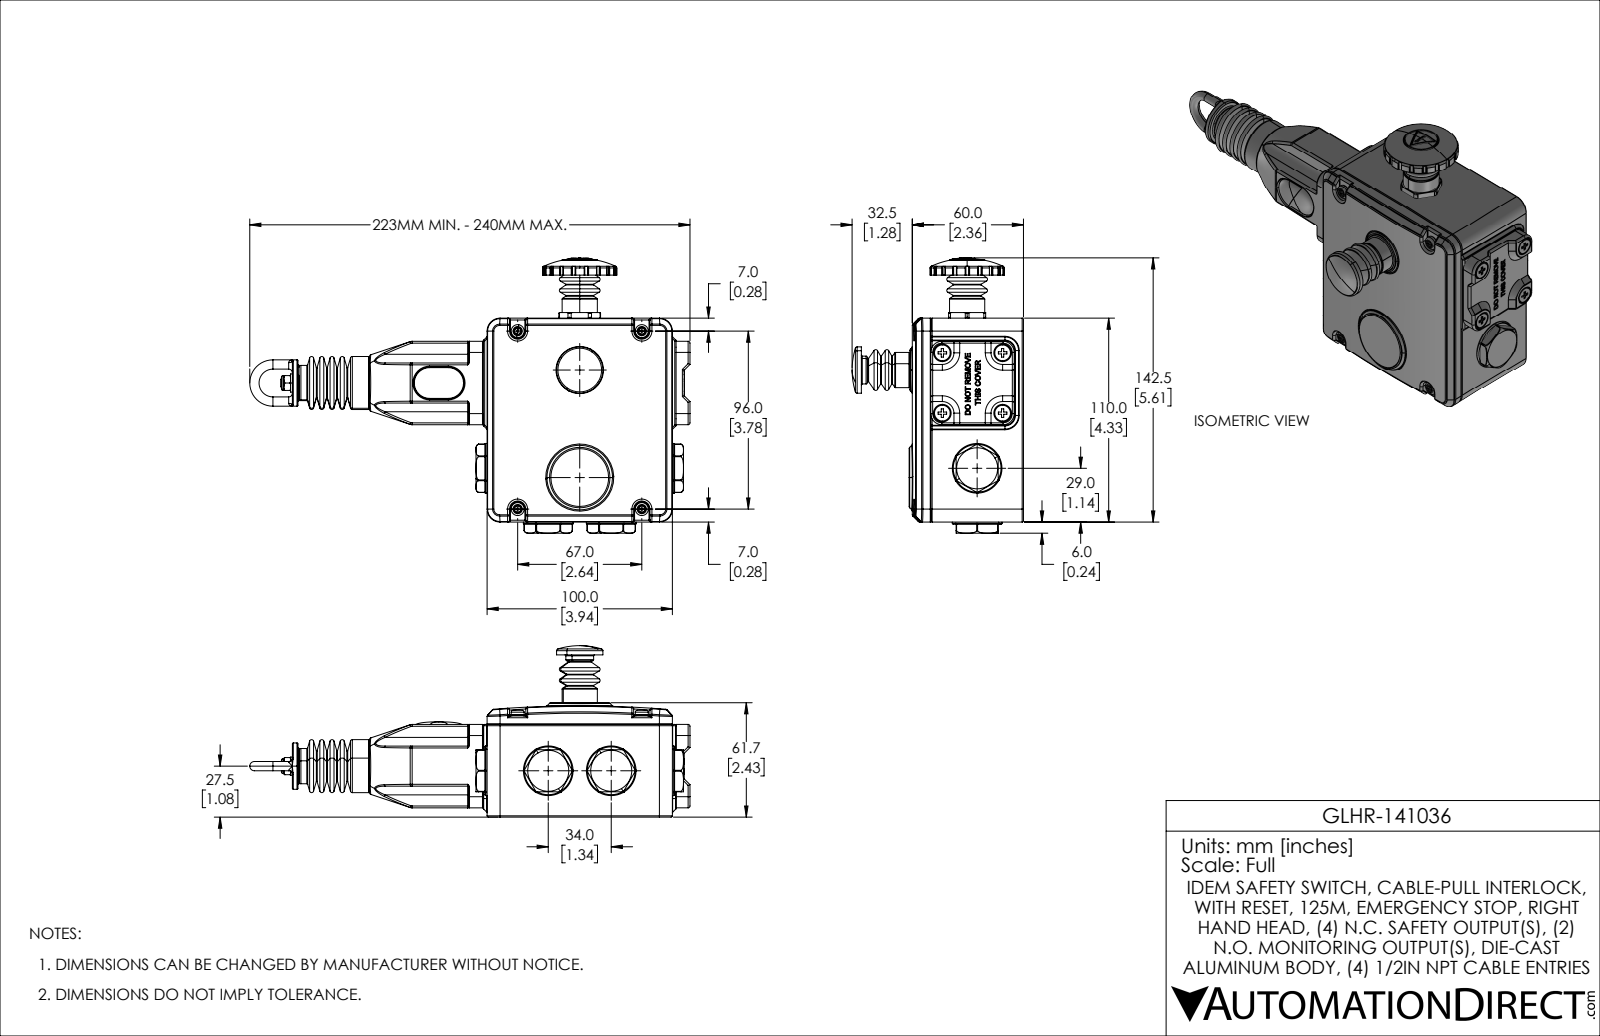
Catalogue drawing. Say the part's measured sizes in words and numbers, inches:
The part is named "GLHR-141036". Its 3-D file was written by "SolidWorks 2021 (AUTOMOTIVE_DESIGN)". It is 32 solids with 4131 faces: 1092 planar, 1371 cylindrical and 1668 other. Overall it measures 9.354 by 5.847 by 3.642 inches. Its volume is 18.02 cubic inches and its surface area 275.6 square inches. Round holes: 11 of diameter 0.197, 9 of diameter 0.209, 7 of diameter 0.374, 6 of diameter 0.354, 4 of diameter 0.13, 4 of diameter 0.157, 4 of diameter 0.189, 4 of diameter 0.213, 4 of diameter 0.228, 3 of diameter 0.118, 3 of diameter 0.173, 3 of diameter 0.504. Round bosses or shafts: 7 of diameter 0.335, 7 of diameter 0.236, 7 of diameter 0.173, 6 of diameter 0.197, 5 of diameter 0.276, 4 of diameter 0.138, 4 of diameter 0.051, 3 of diameter 1.055. Partial cylindrical surfaces (rounded edges, fillets, slot ends): 226 of radius 0.02, 154 of radius 0.039, 136 of radius 0.008, 72 of radius 0.028, 20 of radius 0.012, 14 of radius 0.006, 12 of radius 0.236, 11 of radius 0.004. The main face-to-face distances are 0.138, 2.157, 0.114, 2.043, 4.331, 0.055, 0.157, 4.016, 3.878, 0.079. The hole center spacings are 1.28, 1.281, 0.374, 0.905, 1.891, 1.913, 3.012, 3.489.
